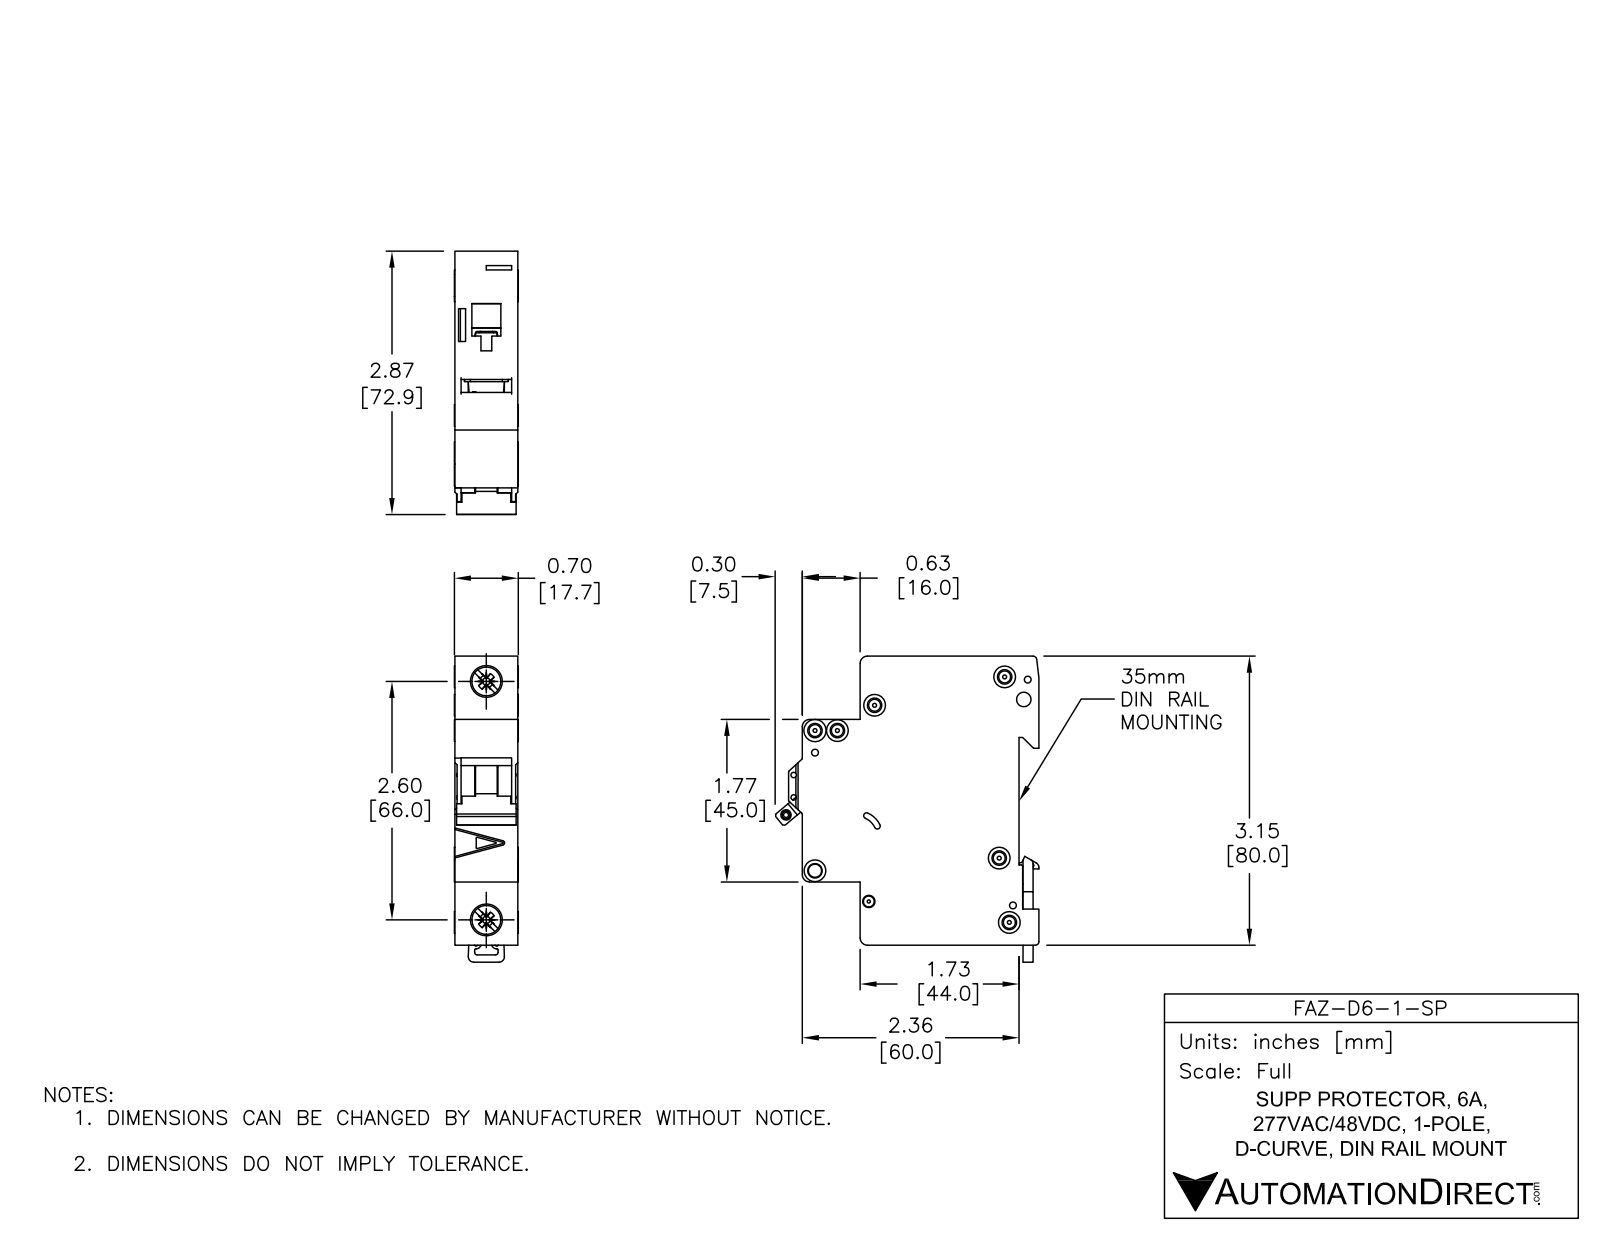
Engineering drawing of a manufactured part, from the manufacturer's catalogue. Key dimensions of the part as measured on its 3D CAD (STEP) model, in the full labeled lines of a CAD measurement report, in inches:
Part name (STEP PRODUCT): FAZ-D6-1-SP
STEP written by: SolidWorks 2014 (AUTOMOTIVE_DESIGN)
Units: inches
Bodies: 5 solids, 558 faces (235 planar, 202 cylindrical, 121 other)
Overall size (bounding box): 3.338 × 2.876 × 0.697
Volume: 4.573 in³ · Surface area: 30.29 in²
Round holes (diameter × count): ⌀0.142 ×6, ⌀0.075 ×3, ⌀0.043 ×2, ⌀0.059 ×2, ⌀0.157 ×2, ⌀0.281 ×2, ⌀0.085 ×1, ⌀0.087 ×1, ⌀0.1 ×1, ⌀0.13 ×1, ⌀0.134 ×1
Round bosses / shafts (diameter × count): ⌀0.236 ×4, ⌀0.323 ×2, ⌀0.098 ×1
Partial cylindrical surfaces — rounded edges, fillets, slot ends (radius × count): R0.01 ×30, R0.02 ×13, R0.079 ×8, R0.008 ×5, R0.039 ×4, R0.031 ×2, R0.118 ×2, R0.059 ×1
Main face-to-face distances: 0.689, 3.129, 0.217, 1.949, 1.732, 2.579, 2.362, 0.63, 0.069, 0.62
Hole centre spacings: 0.244, 0.537, 0.189, 0.204, 0.221, 0.24, 0.254, 0.322
